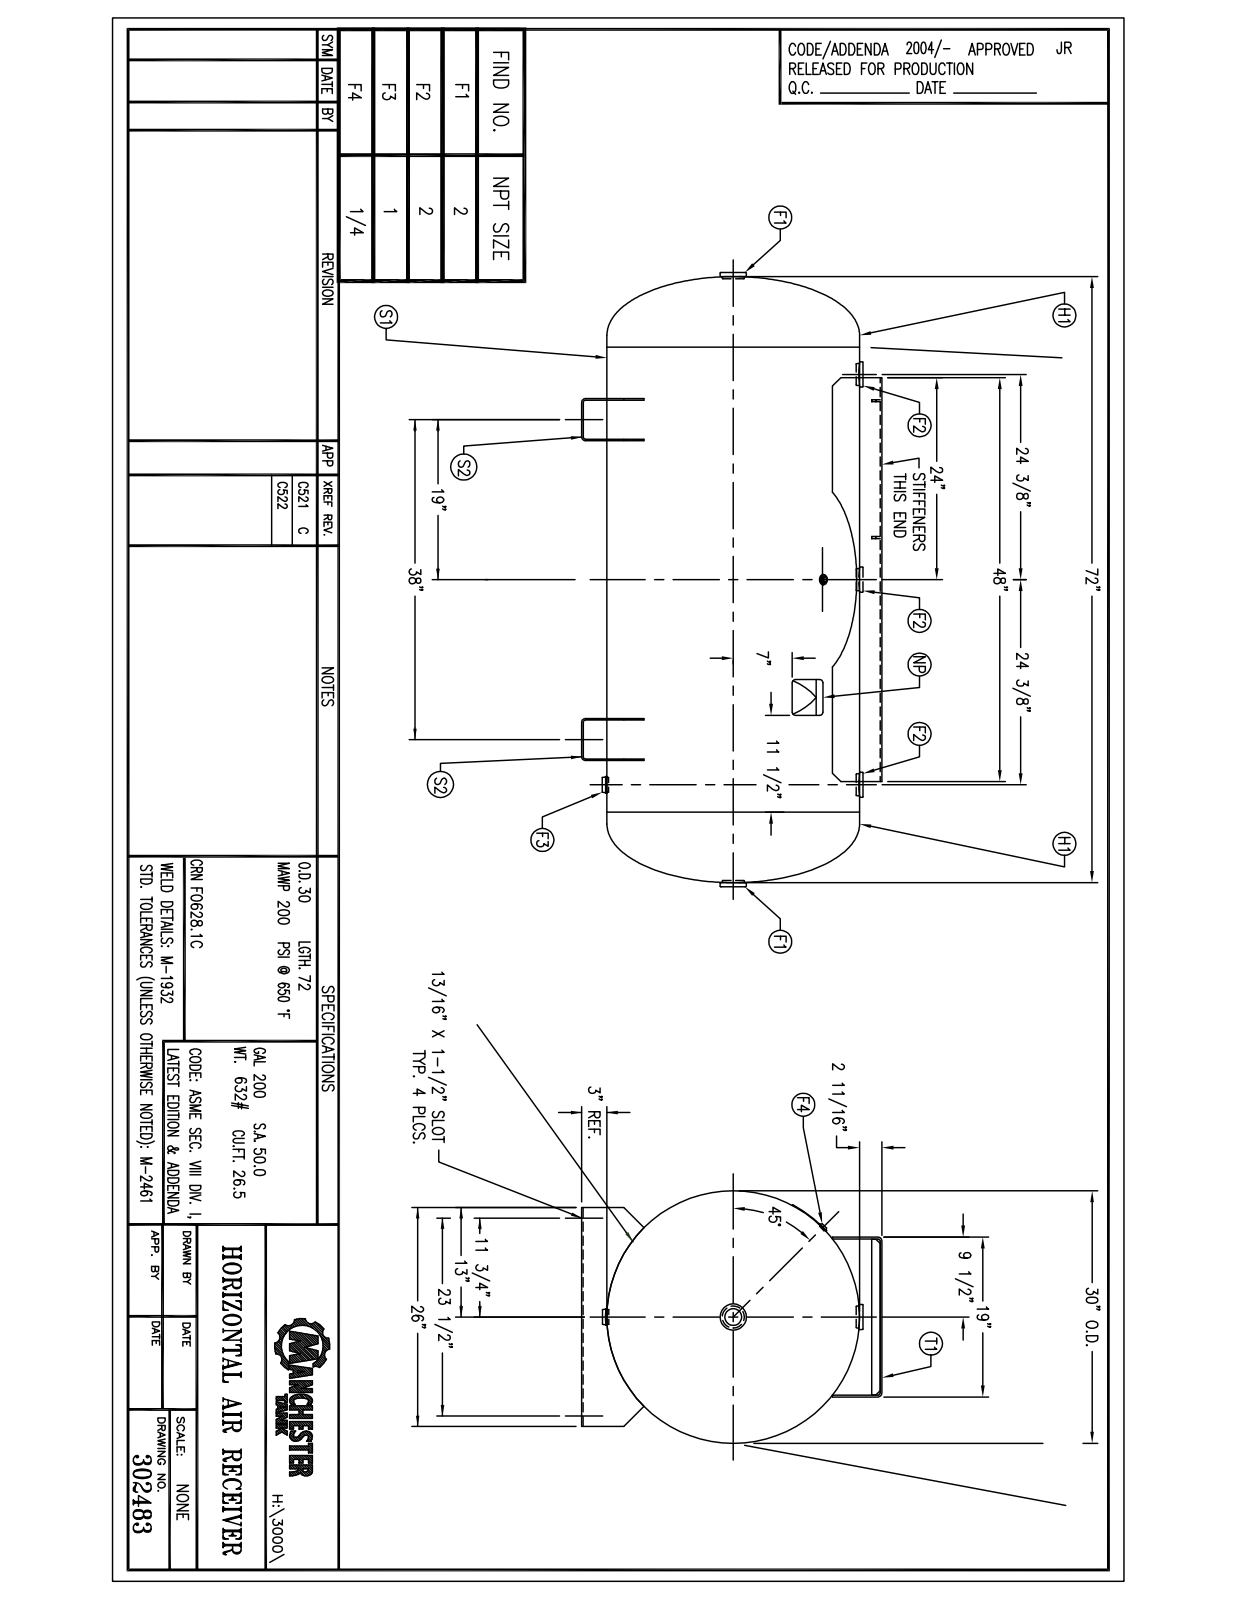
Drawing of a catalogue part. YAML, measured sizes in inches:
part_name: "302483"
step_written_by: "SolidWorks 2011 (CONFIG_CONTROL_DESIGN)"
units: inches
bodies: {solids: 0, faces: 232, planar: 88, cylindrical: 86, other: 58}
overall_size: [73.25, 35.714, 30]
round_holes:
  - {diameter: 2.375, count: 4}
  - {diameter: 0.54, count: 1}
  - {diameter: 1.315, count: 1}
  - {diameter: 3.5, count: 1}
  - {diameter: 29.546, count: 1}
round_bosses_or_shafts:
  - {diameter: 3.625, count: 2}
  - {diameter: 30, count: 1}
  - {diameter: 29.63, count: 1}
  - {diameter: 3.5, count: 1}
  - {diameter: 2.875, count: 1}
  - {diameter: 1.5, count: 1}
partial_cylinders:
  - {radius: 0.406, count: 8}
  - {radius: 0.5, count: 6}
  - {radius: 0.094, count: 4}
  - {radius: 0.281, count: 4}
  - {radius: 1.75, count: 2}
  - {radius: 15.06, count: 1}
  - {radius: 17.892, count: 1}
face_to_face_distances: [0.25, 38, 0.187, 5.813, 18.75, 0.188, 35.465, 35.715, 35.277, 35.527]
hole_center_spacings: [24.375, 48.75]
